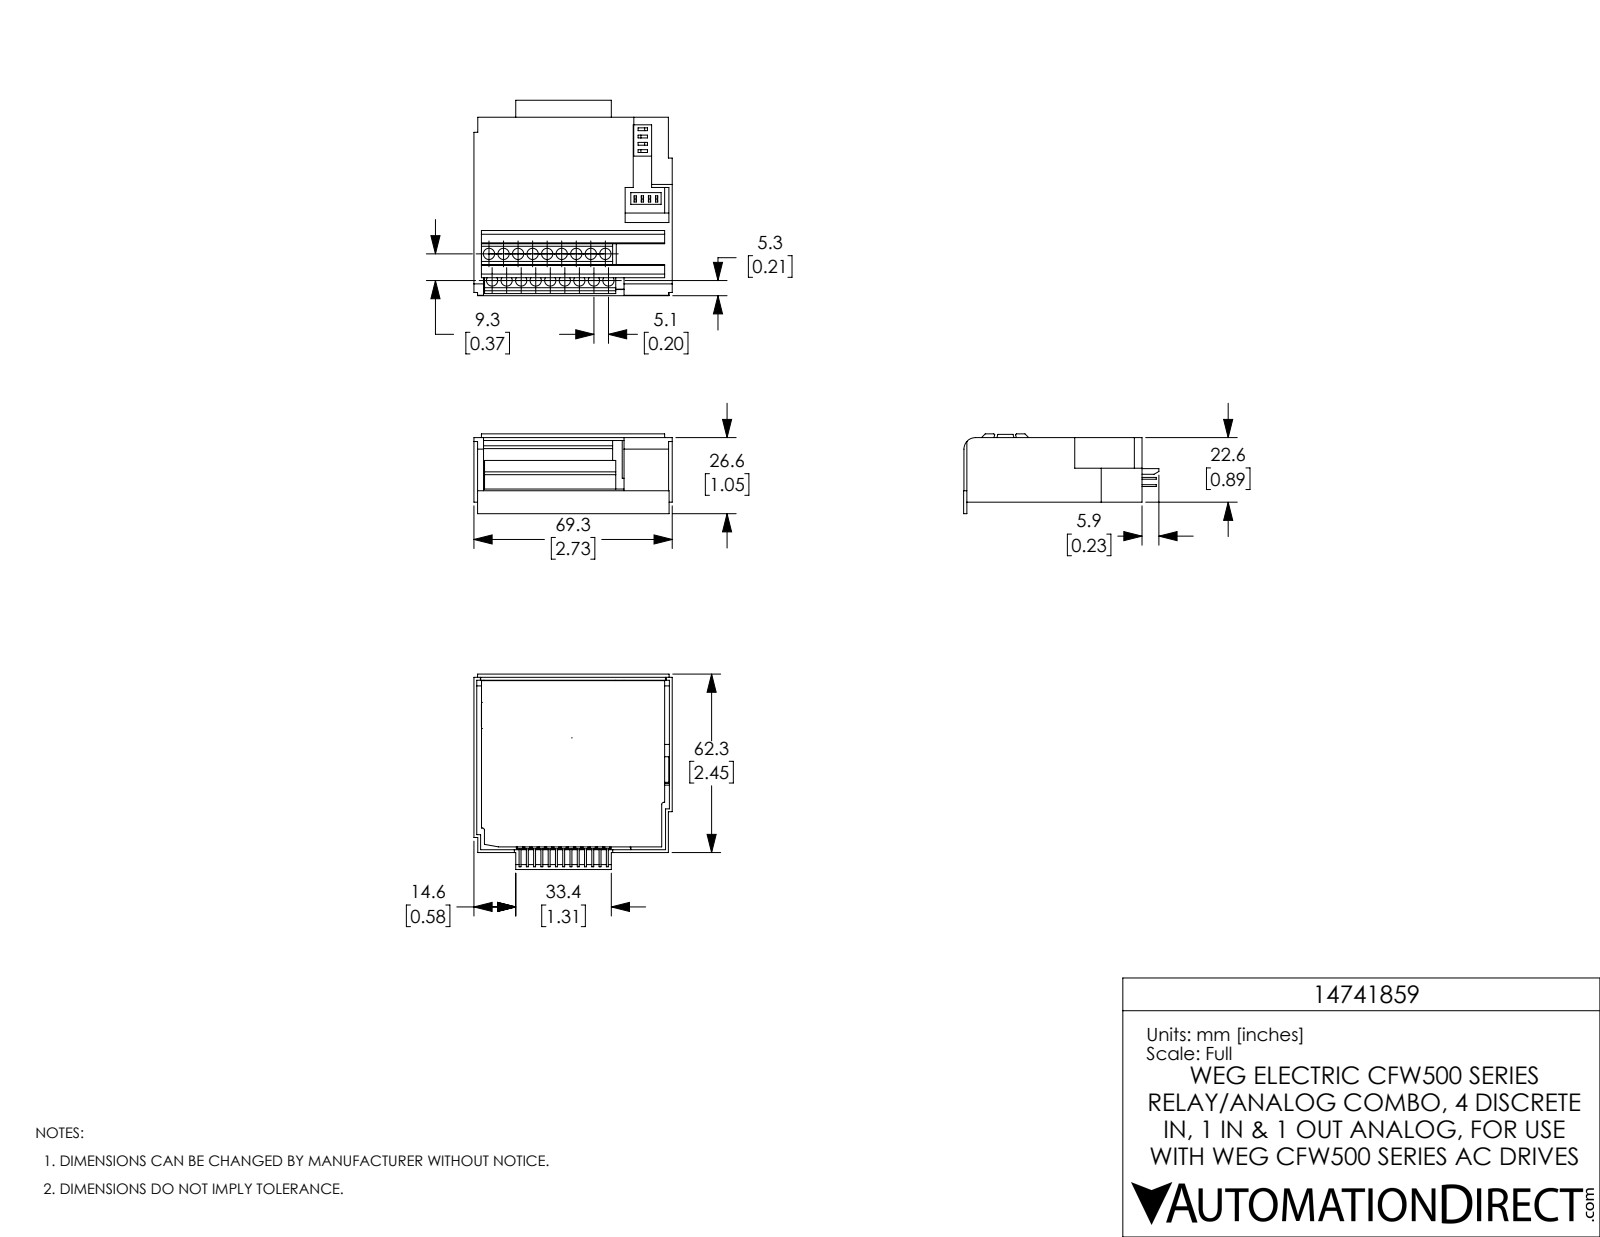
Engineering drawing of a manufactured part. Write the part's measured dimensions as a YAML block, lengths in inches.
part_name: "14741859_MODULO IO CFW500_IOS Coord nc"
step_written_by: "SolidWorks 2017 (AUTOMOTIVE_DESIGN)"
units: inches
bodies: {solids: 2, faces: 494, planar: 452, cylindrical: 42, other: 0}
overall_size: [2.726, 2.685, 1.096]
volume: 1.65
surface_area: 46.89
round_holes:
  - {diameter: 0.154, count: 9}
  - {diameter: 0.155, count: 9}
partial_cylinders:
  - {radius: 0.03, count: 2}
  - {radius: 0.118, count: 1}
  - {radius: 0.157, count: 1}
face_to_face_distances: [0.039, 0.063, 0.73, 0.667, 0.707, 0.77, 2.687, 2.727, 0.051, 2.413]
hole_center_spacings: [0.2, 0.4, 0.6, 0.8, 0.369, 0.399, 0.44, 1]
